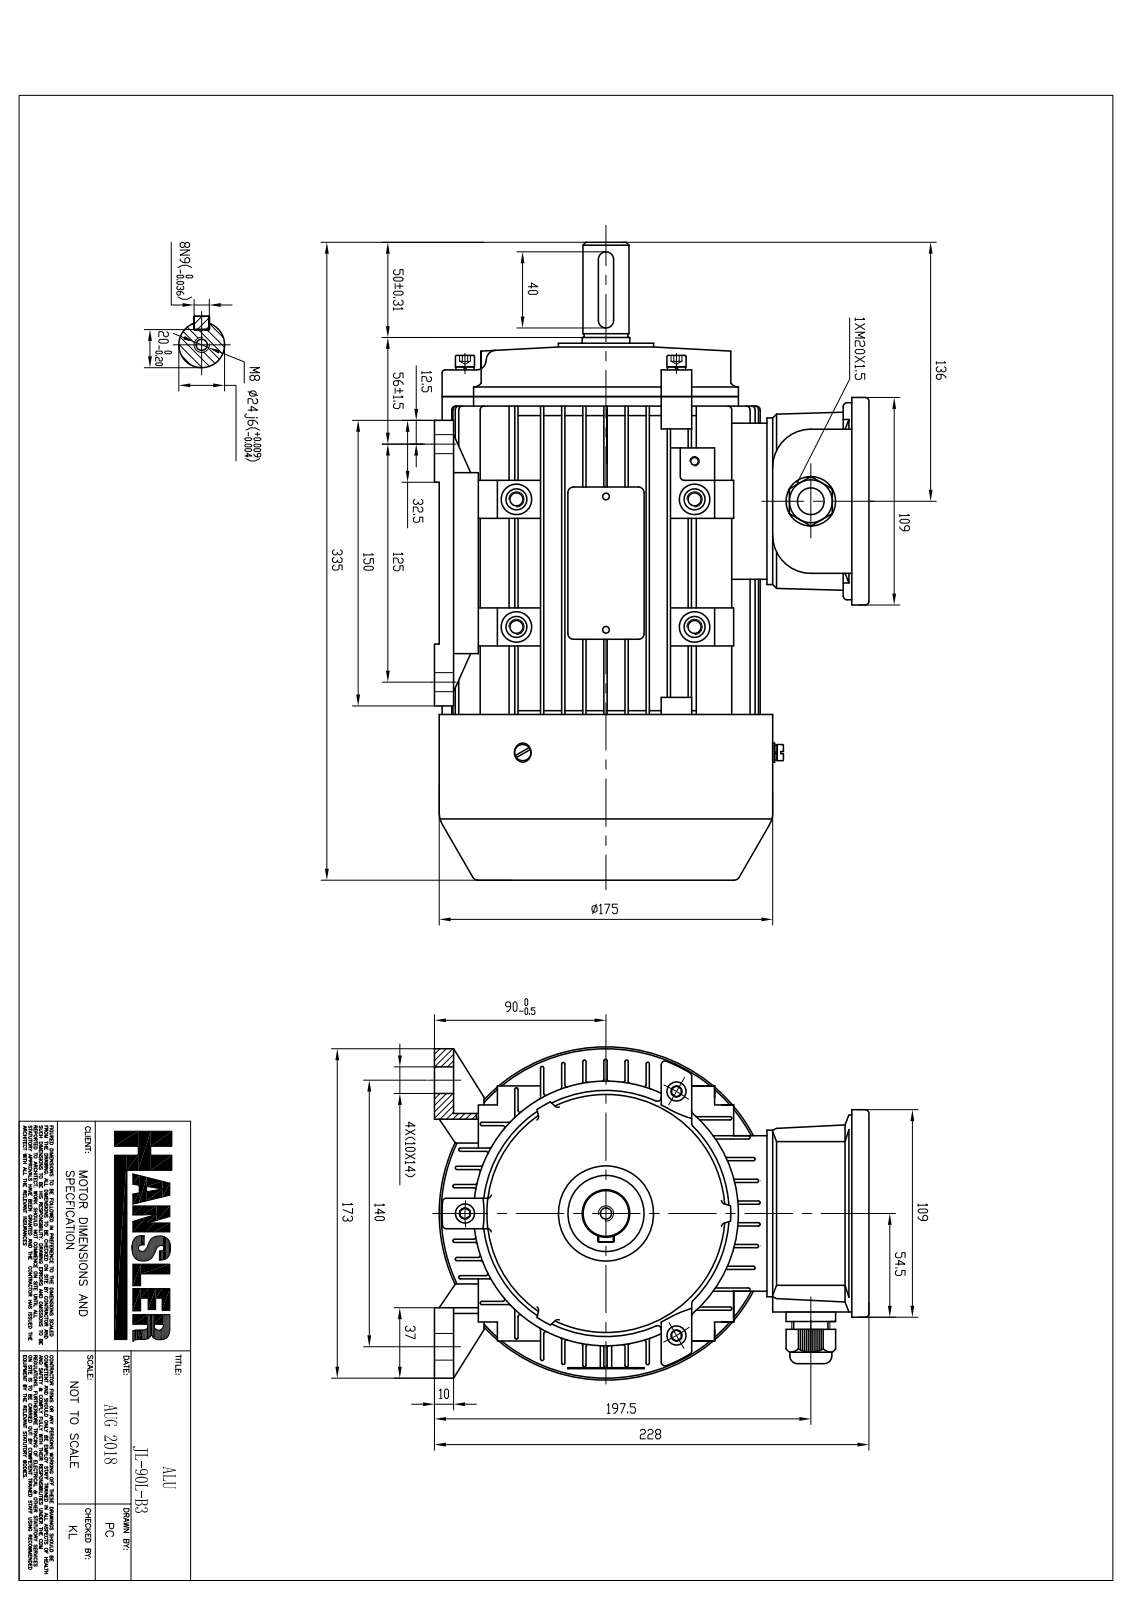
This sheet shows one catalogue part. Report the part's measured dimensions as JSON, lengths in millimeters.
{"part_name": "JL-90L-B3", "step_written_by": "SIEMENS PLM Software NX 12.0 (AP203_CONFIGURATION_CONTROLLED_3D_DESIGN_OF_MECHANICAL_PARTS_AND_ASSEMBLIES_MIM_LF)", "units": "millimeters", "bodies": {"solids": 54, "faces": 4335, "planar": 2712, "cylindrical": 1240, "other": 383}, "overall_size": [335, 230.5, 175], "volume_mm3": 1342000, "surface_area_mm2": 881116, "round_holes": [[4, 13], [5, 11], [5.8, 10], [8, 10], [16, 8], [4.8, 4], [5.25, 4], [5.3, 4], [8.58, 4], [9, 4], [12, 4], [6, 3]], "round_bosses_or_shafts": [[11, 8], [4.48, 8], [15, 4], [14.79, 4], [13, 4], [12, 4], [10, 4], [7.85, 4]], "partial_cylinders_radius": [[0.5, 464], [1, 72], [2, 40], [4, 19], [0.75, 16], [5, 16], [3, 11], [7, 8]], "face_to_face_distances": [1.7, 11.08, 44.32, 22.16, 2.5, 9.38, 33.24, 2, 55.4, 42.62], "hole_center_spacings": [35.51, 50.8, 57.1, 72.54, 77.07, 22, 15, 15.56]}
